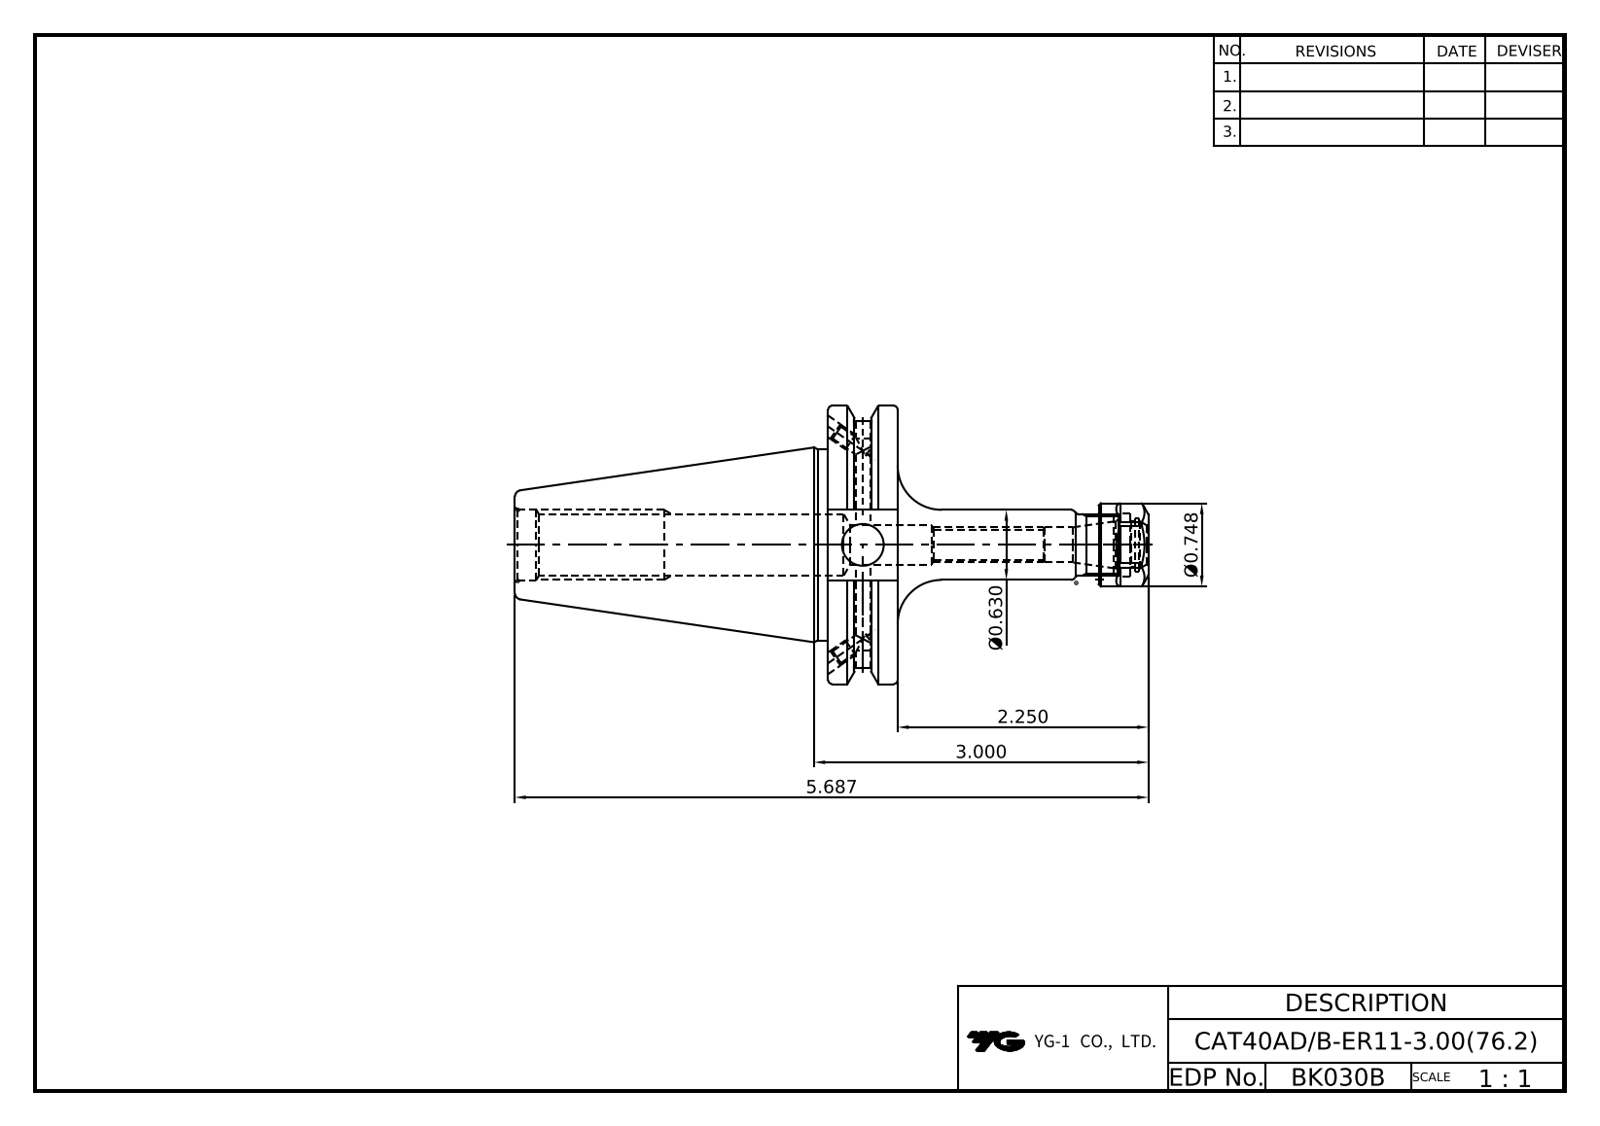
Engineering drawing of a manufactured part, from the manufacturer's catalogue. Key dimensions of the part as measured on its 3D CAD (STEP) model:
Part name (STEP PRODUCT): LO-CAT40ADB-ER11-3.00; ER11NUT
STEP written by: Autodesk Inventor 2024 (AUTOMOTIVE_DESIGN)
Units: millimetres
Bodies: 2 solids, 109 faces (51 planar, 32 cylindrical, 26 other)
Overall size (bounding box): 144.45 × 63.5 × 61.09
Volume: 111 443 mm³ · Surface area: 25 624 mm²
Round holes (diameter × count): ⌀3.24 ×4, ⌀4 ×2, ⌀4.2 ×2, ⌀6.4 ×1, ⌀8 ×1, ⌀8.6 ×1, ⌀9 ×1, ⌀9.53 ×1, ⌀13.39 ×1, ⌀14 ×1, ⌀16.3 ×1
Round bosses / shafts (diameter × count): ⌀63.5 ×1, ⌀43.6 ×1, ⌀19 ×1, ⌀16 ×1
Partial cylindrical surfaces — rounded edges, fillets, slot ends (radius × count): R28.15 ×1
Main face-to-face distances: 15.88, 17, 47.6, 16.38, 71.42, 87.3, 144.45, 73.03, 57.15, 81.29
Hole centre spacings: 0.35
